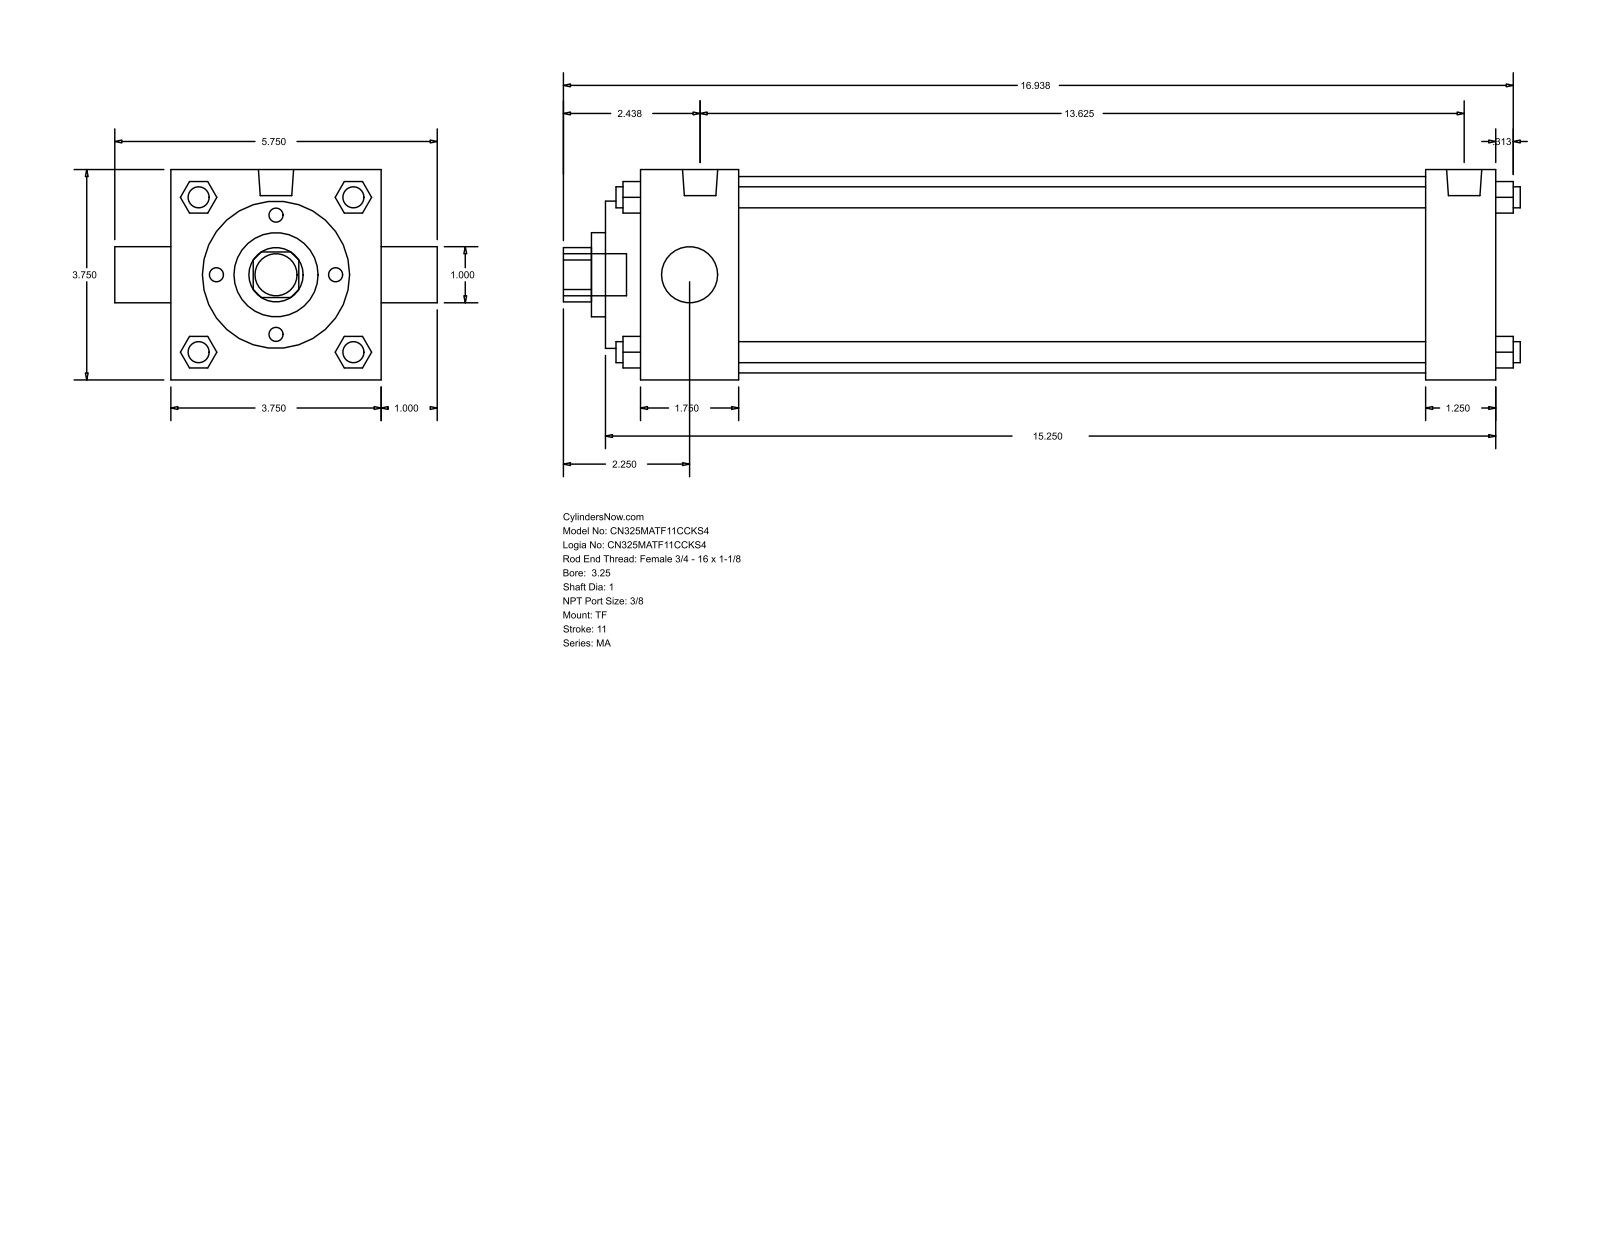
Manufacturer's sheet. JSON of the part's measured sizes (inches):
{"part_name": "MA_TF__0325_1", "step_written_by": "GSSL Pune (CONFIG_CONTROL_DESIGN)", "units": "inches", "bodies": {"solids": 0, "faces": 122, "planar": 93, "cylindrical": 29, "other": 0}, "overall_size": [17.063, 5.75, 3.75], "round_holes": [[1, 2], [1.5, 1], [2.625, 1], [3.5, 1]], "round_bosses_or_shafts": [[0.375, 4], [0.437, 3], [0.627, 2], [0.75, 1]], "partial_cylinders_radius": [[0.484, 1]], "face_to_face_distances": [3.75, 15.25, 15.875, 0.625, 1.75, 14, 12.25, 13.5, 1.25, 2.375]}
